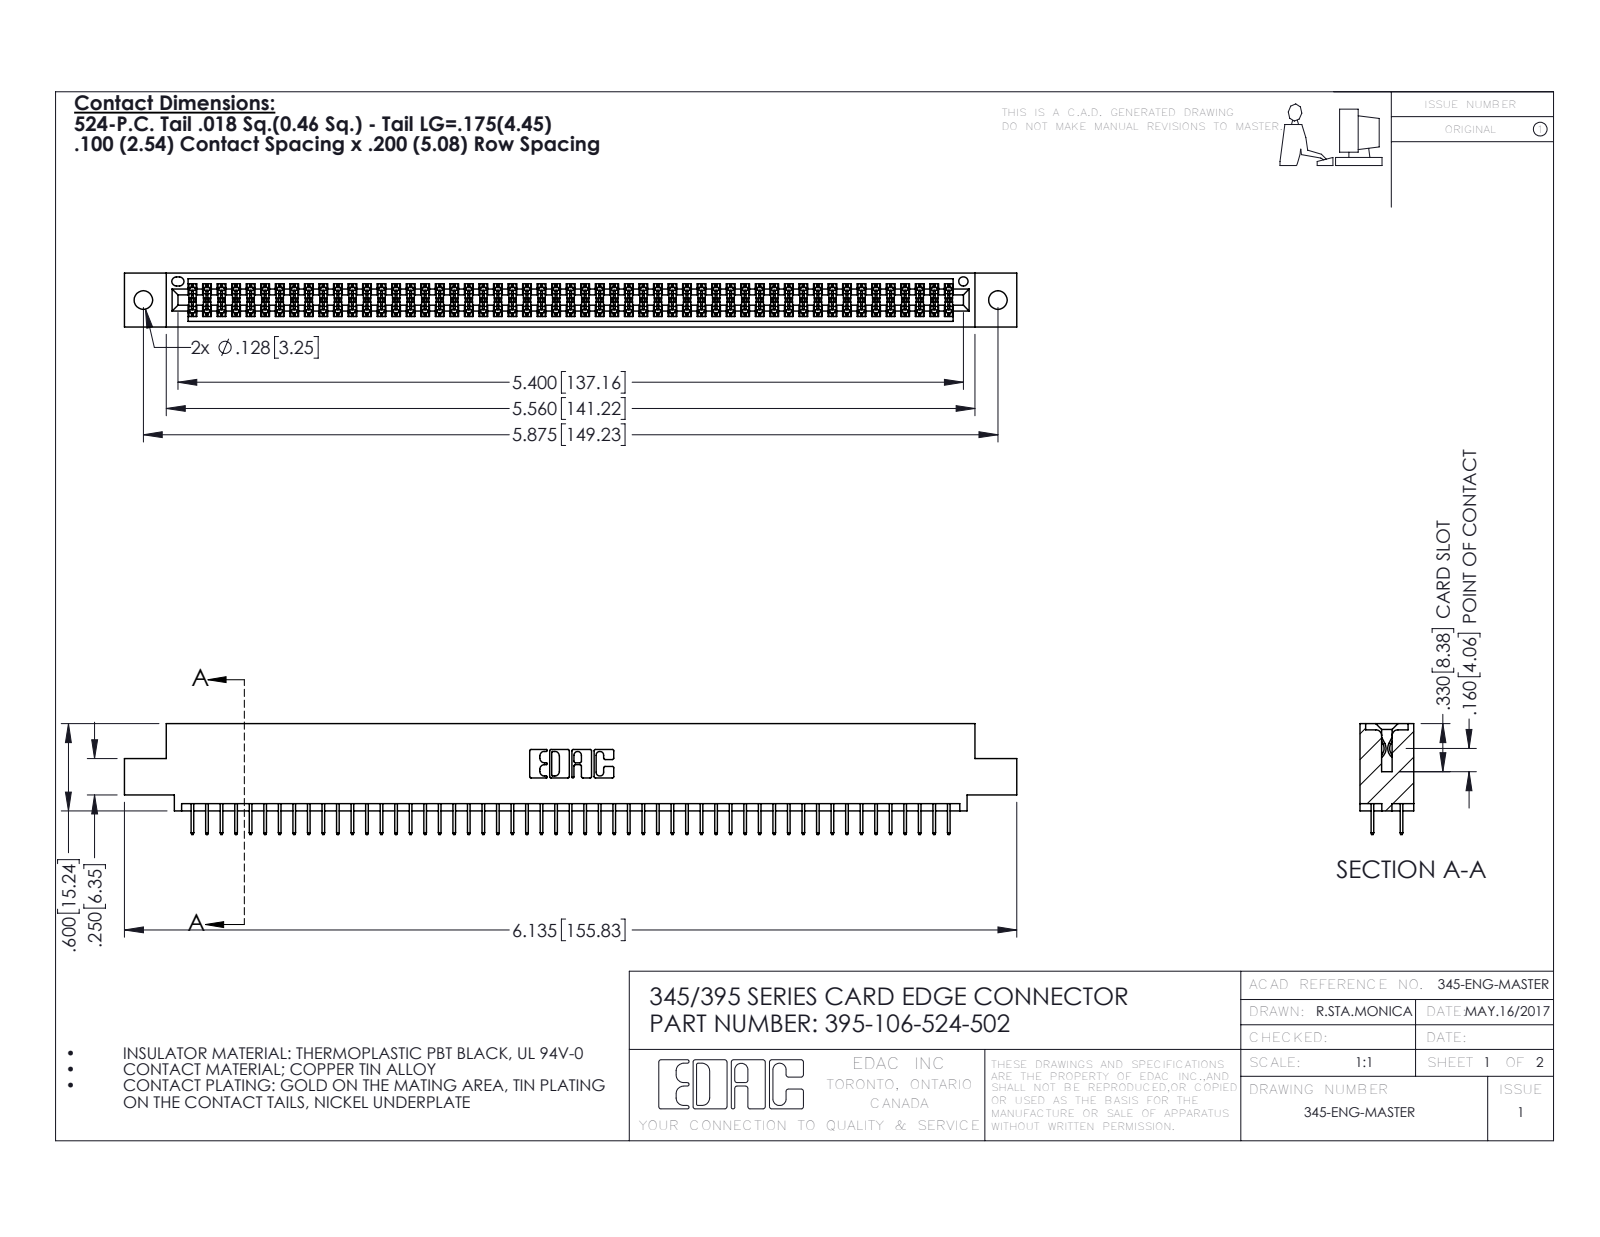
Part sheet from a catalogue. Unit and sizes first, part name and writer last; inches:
Units: inches
Overall size (bounding box): 6.135 × 0.762 × 0.37
Round holes (diameter × count): ⌀0.128 ×2, ⌀0.064 ×1
Partial cylindrical surfaces — rounded edges, fillets, slot ends (radius × count): R0.006 ×159, R0.01 ×22, R0.007 ×6, R0.031 ×6, R0.026 ×3, R0.014 ×2, R0.019 ×2, R0.022 ×2
Main face-to-face distances: 0.072, 0.298, 0.2, 0.37, 0.098, 0.272, 0.025, 0.225, 0.072, 0.175
Hole centre spacings: 0.27, 5.639, 5.875
Volume: 0.913 in³ · Surface area: 33.69 in²
Bodies: 107 solids, 5854 faces (4218 planar, 1636 cylindrical, 0 other)
Part name (STEP PRODUCT): 345-292-001_345-293-124; 395-106-524-502; 345 Part_0.110 Offset - 0.128 Dia
STEP written by: SolidWorks 2016 (CONFIG_CONTROL_DESIGN)
